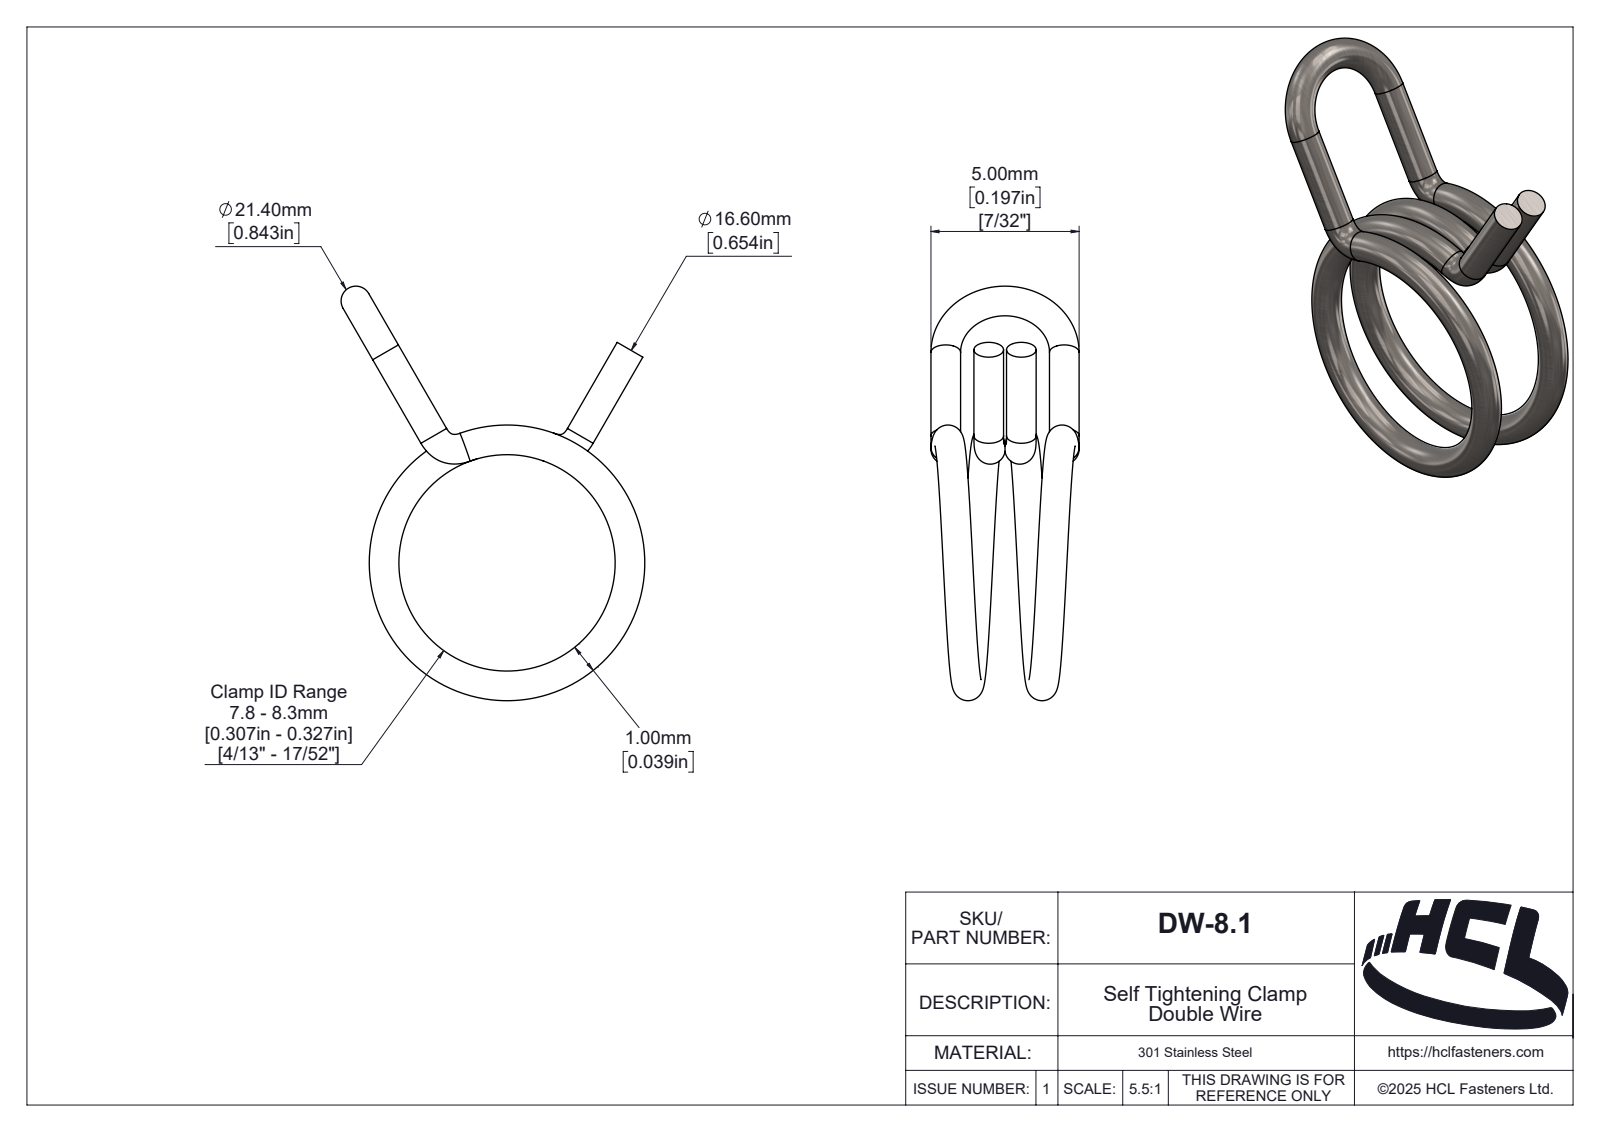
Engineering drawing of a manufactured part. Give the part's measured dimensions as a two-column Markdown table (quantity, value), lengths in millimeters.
| quantity | value |
| --- | --- |
| part name | DW-8.1 |
| STEP written by | SolidWorks 2025 (AUTOMOTIVE_DESIGN) |
| units | millimeters |
| bodies | 1 solid, 125 faces (14 planar, 53 cylindrical, 58 other) |
| overall size | 13.98 × 10.25 × 5 |
| volume | 65 mm³ |
| surface area | 261 mm² |
| round bosses / shafts (diameter × count) | 1 × 4 |
| partial cylindrical surfaces (radius × count) | 0.16 × 1, 0.2 × 1, 0.21 × 1, 0.26 × 1, 0.36 × 1, 0.48 × 1, 0.6 × 1, 0.68 × 1 |
